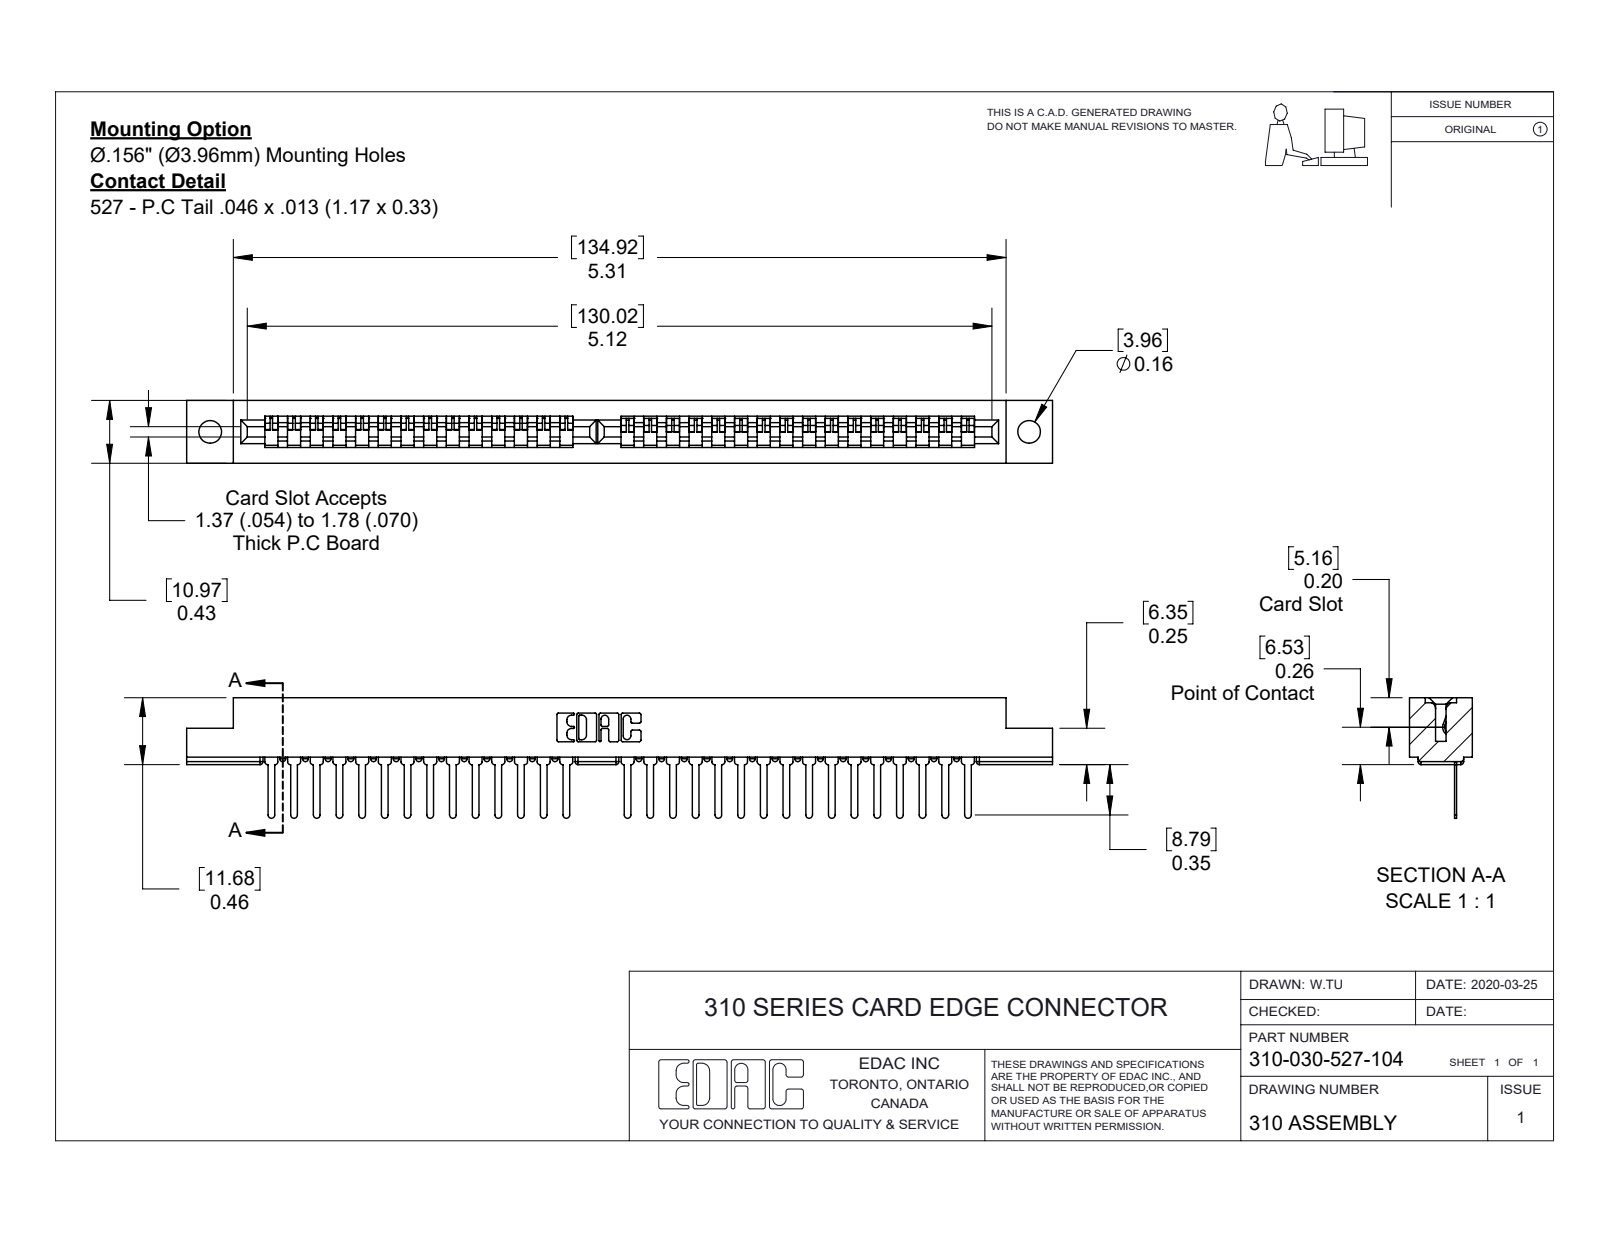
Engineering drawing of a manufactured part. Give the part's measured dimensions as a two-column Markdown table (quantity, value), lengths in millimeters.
| quantity | value |
| --- | --- |
| part name | 310 Part_.156 Dia. Hole; 310-030-527-104; 307-290-001_527 |
| STEP written by | SolidWorks 2016 (CONFIG_CONTROL_DESIGN) |
| units | millimeters |
| bodies | 31 solids, 1846 faces (1194 planar, 588 cylindrical, 64 other) |
| overall size | 151.21 × 21.06 × 10.97 |
| volume | 12 600 mm³ |
| surface area | 14 865 mm² |
| round holes (diameter × count) | 3.96 × 2 |
| partial cylindrical surfaces (radius × count) | 0.51 × 158, 0.58 × 30, 0.25 × 22, 0.17 × 6, 0.8 × 6, 0.67 × 3, 0.3 × 2, 0.64 × 2 |
| main face-to-face distances | 2.76, 8.22, 10.98, 0.38, 0.33, 1.82, 10.38, 5.46, 3.14, 7.84 |
| hole center spacings | 143 |
